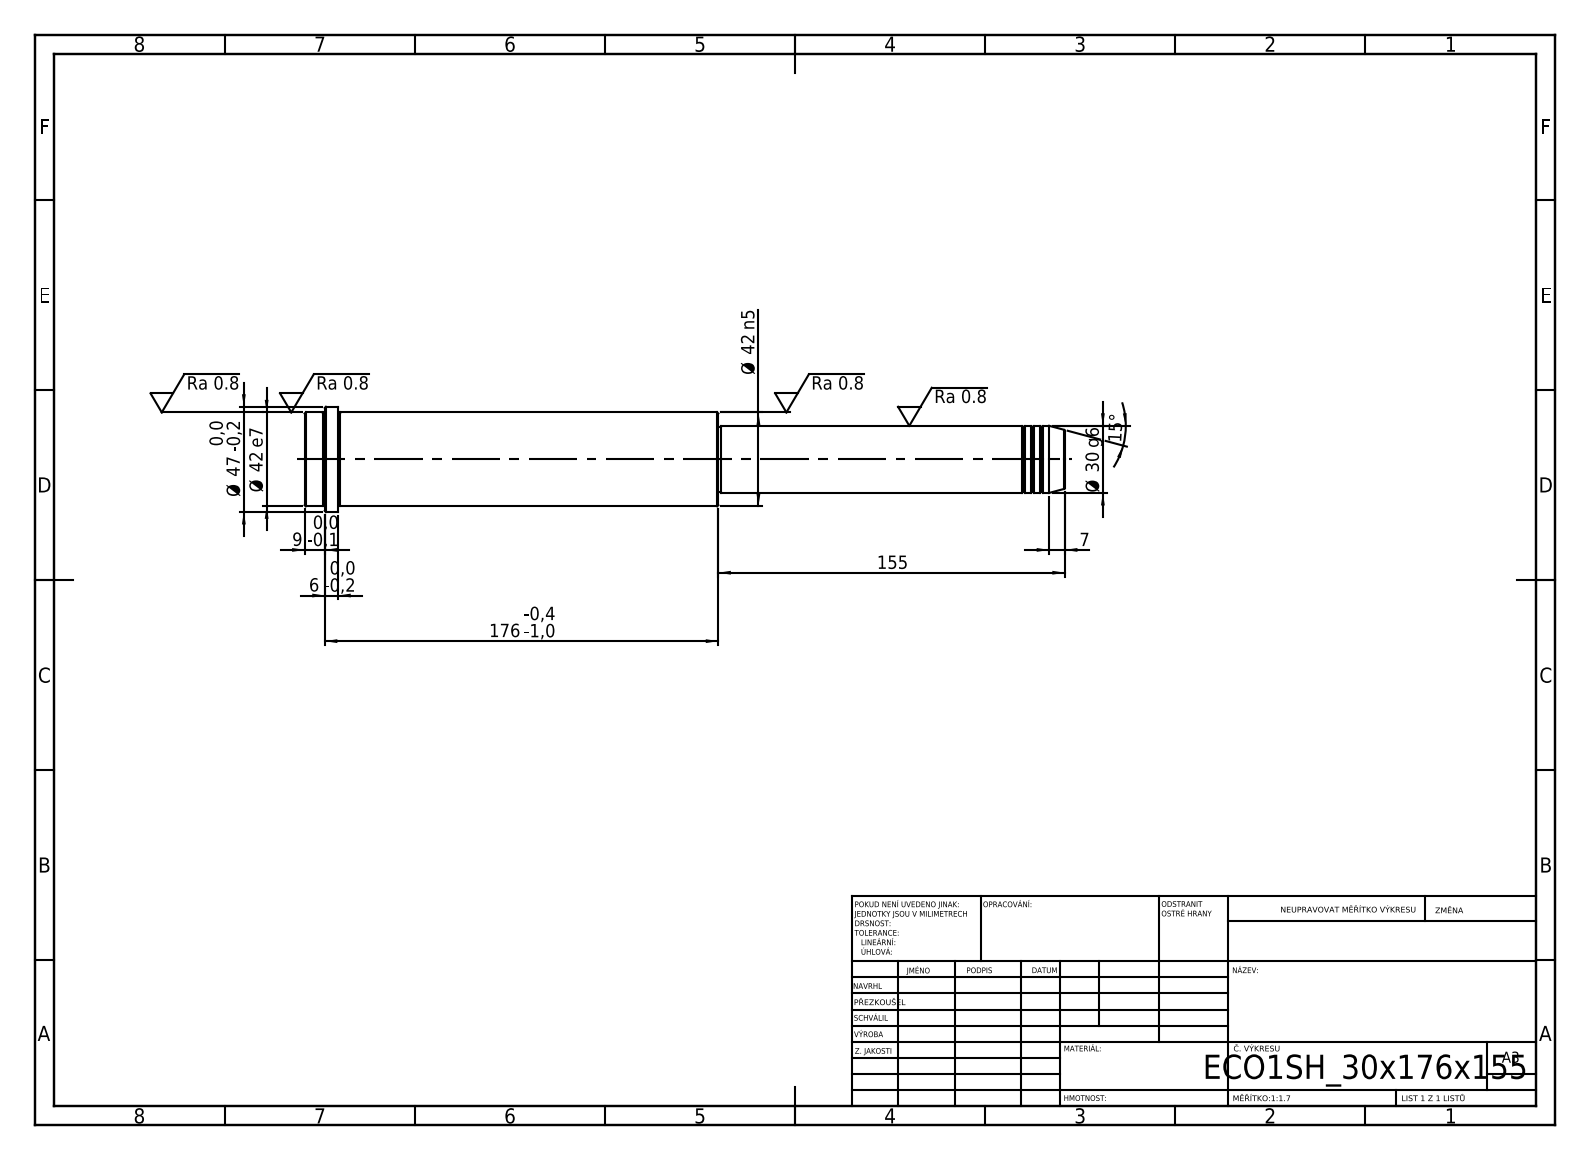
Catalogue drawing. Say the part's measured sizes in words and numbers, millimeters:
Its 3-D file was written by "SolidWorks 2019 (CONFIG_CONTROL_DESIGN)". It is 1 solid with 52 faces: 6 planar, 16 cylindrical and 30 other. Overall it measures 340 by 47 by 47 millimeters. Its volume is 367 062 cubic millimeters and its surface area 42 653 square millimeters. Round bosses or shafts: 1 of diameter 47, 1 of diameter 42, 1 of diameter 30, 1 of diameter 29. The main face-to-face distances are 185, 155, 340, 325, 170, 15, 331, 176, 6, 9.
